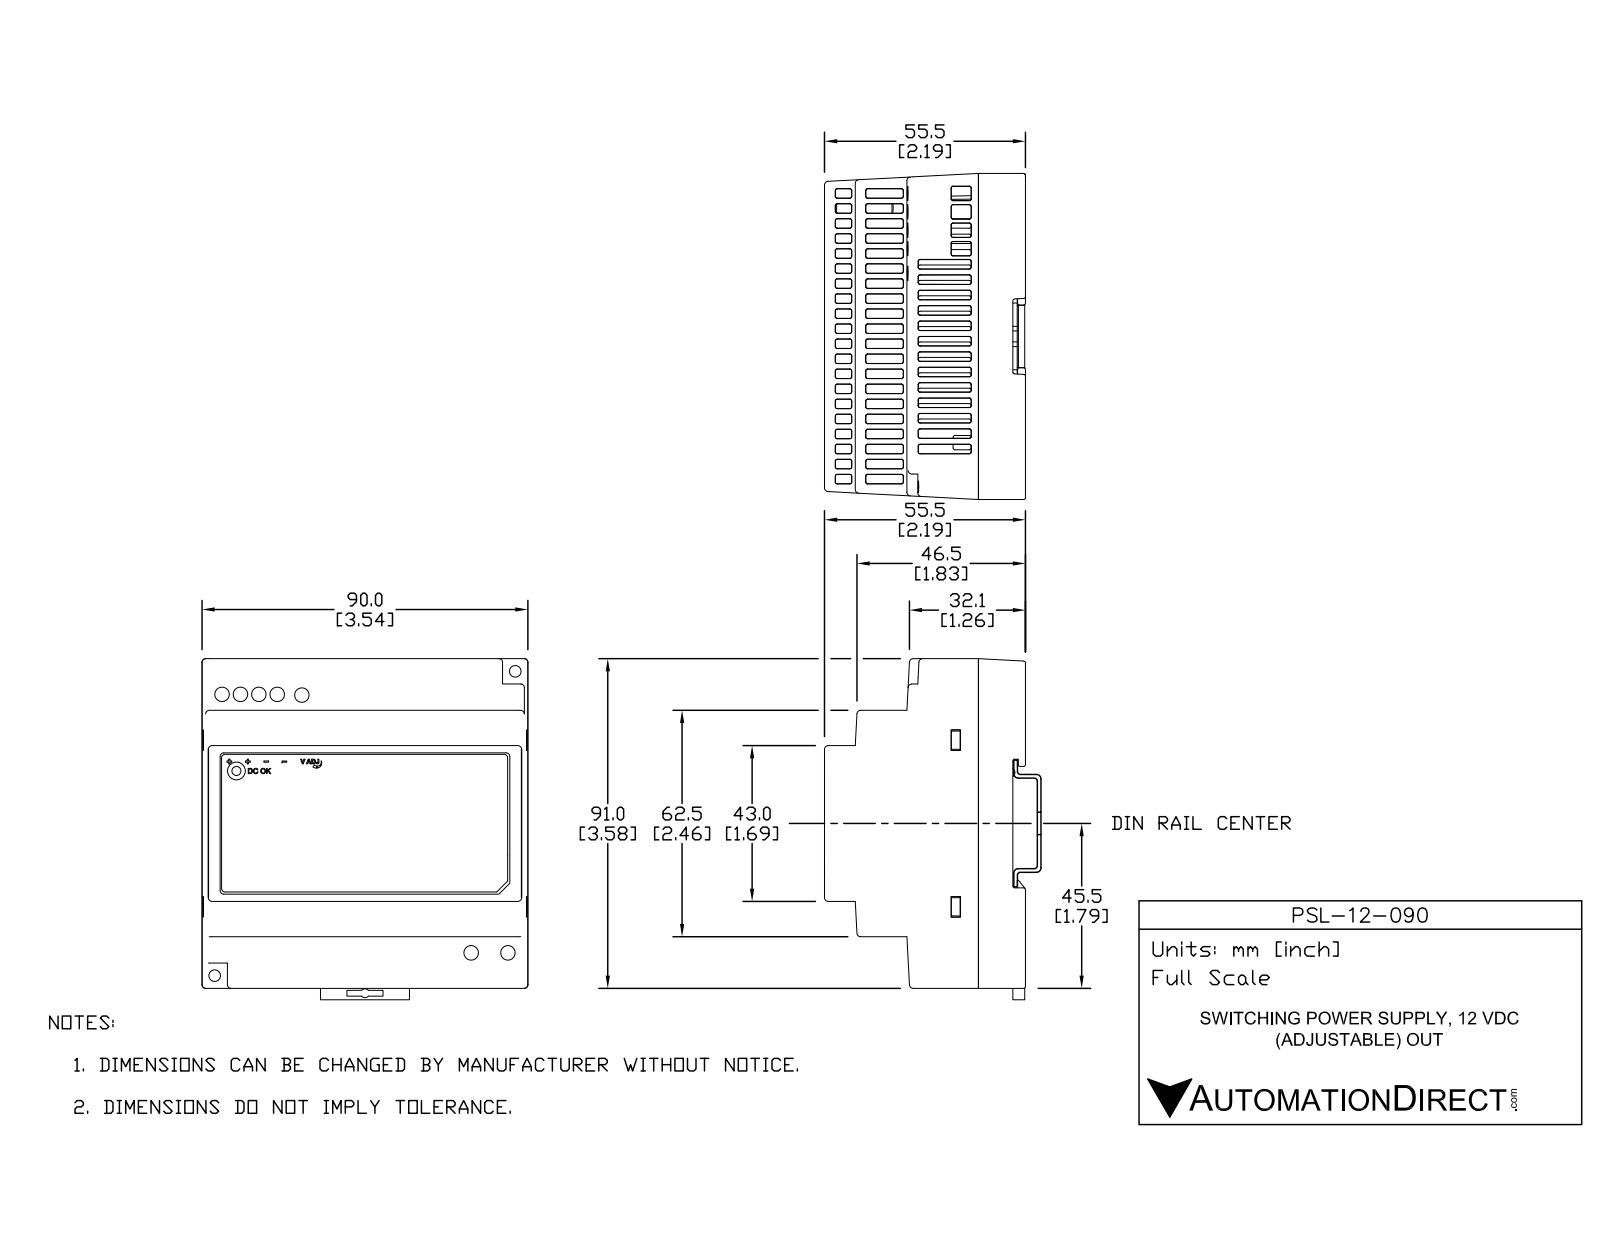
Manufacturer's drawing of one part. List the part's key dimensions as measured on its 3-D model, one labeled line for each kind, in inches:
Part name (STEP PRODUCT): PSL-12-090
STEP written by: SolidWorks 2017 (AUTOMOTIVE_DESIGN)
Units: inches
Bodies: 4 solids, 1701 faces (817 planar, 722 cylindrical, 162 other)
Overall size (bounding box): 3.707 × 3.543 × 2.185
Volume: 3.826 in³ · Surface area: 110.3 in²
Round holes (diameter × count): ⌀0.098 ×2, ⌀0.126 ×2, ⌀0.157 ×1, ⌀0.209 ×1, ⌀0.217 ×1
Round bosses / shafts (diameter × count): ⌀0.236 ×1, ⌀0.156 ×1
Partial cylindrical surfaces — rounded edges, fillets, slot ends (radius × count): R0.02 ×556, R0.039 ×47, R0.008 ×36, R0.016 ×8, R0.04 ×2, R0.059 ×2, R0.128 ×2, R0.048 ×1
Main face-to-face distances: 0.087, 0.079, 1.882, 0.071, 1.969, 2.039, 1.953, 0.541, 0.462, 0.619
Hole centre spacings: 0.277, 4.386, 2.096, 2.237, 2.944, 3.219, 4.125, 4.649
